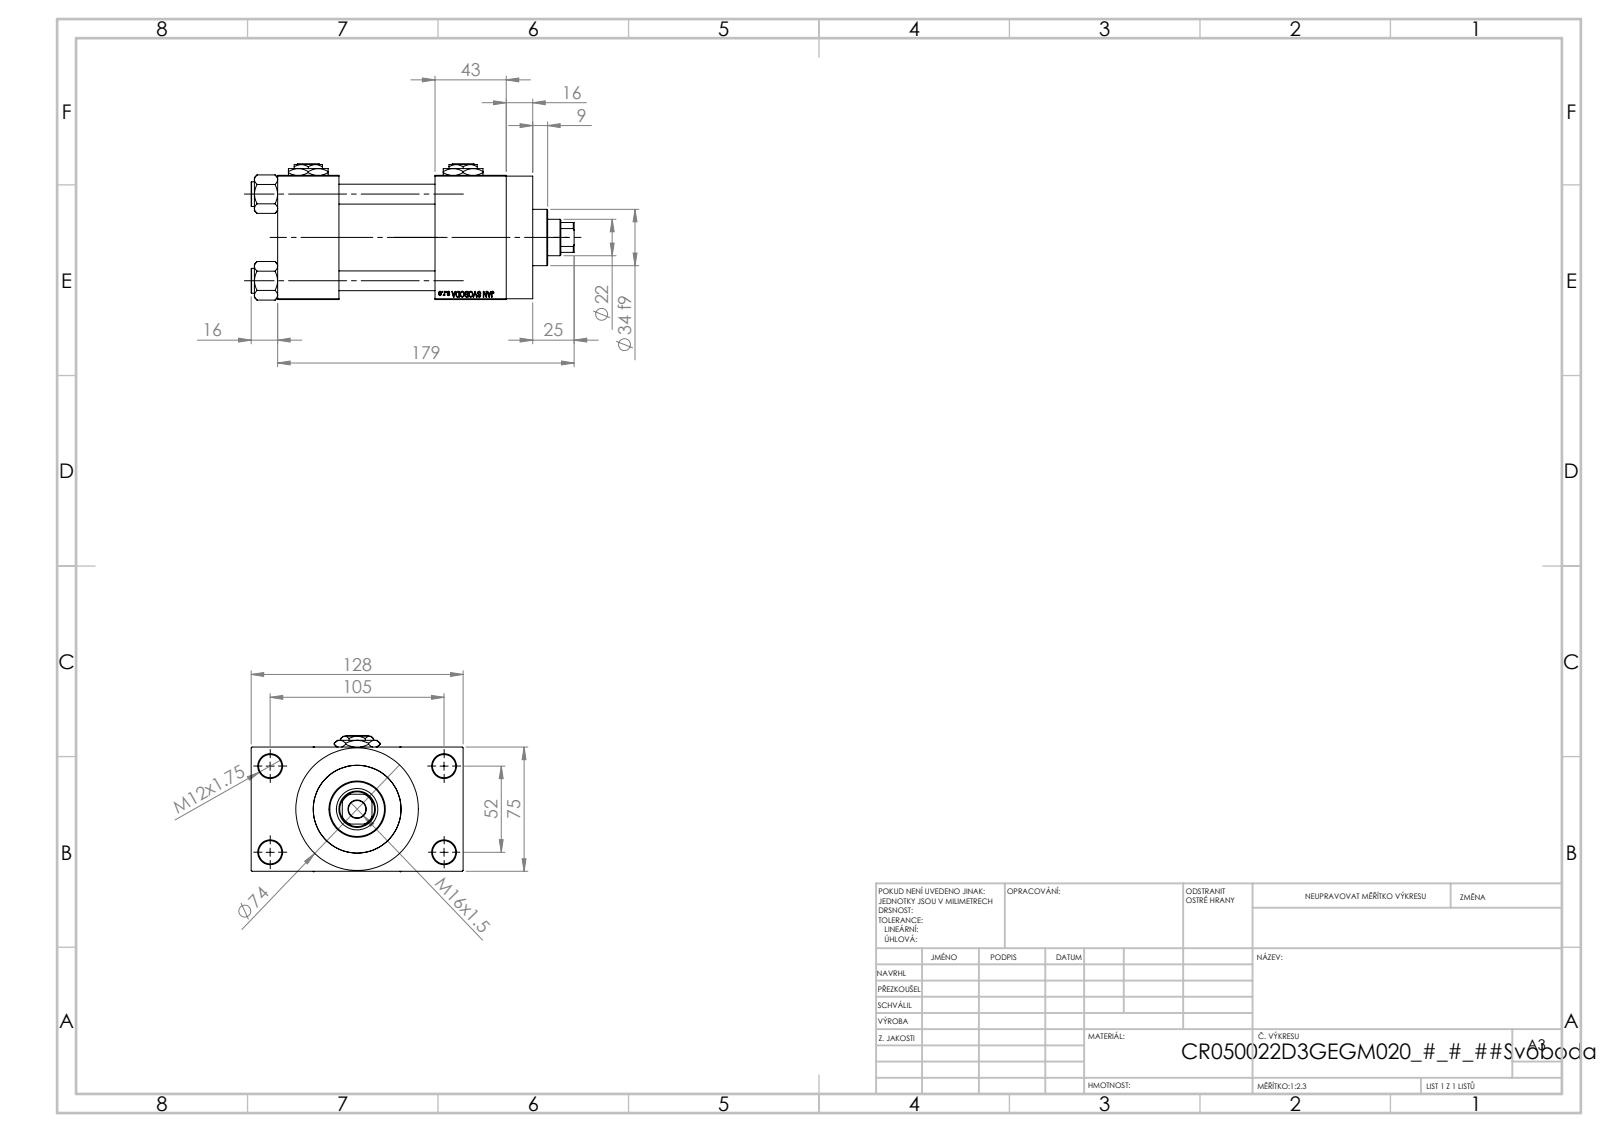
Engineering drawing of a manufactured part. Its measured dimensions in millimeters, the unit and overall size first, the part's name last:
Units: millimetres
Overall size (bounding box): 195 × 128 × 82.27
Round holes (diameter × count): ⌀12 ×4, ⌀14 ×4, ⌀7 ×2, ⌀20.96 ×2, ⌀30 ×2, ⌀10.5 ×1, ⌀22 ×1, ⌀25 ×1, ⌀41 ×1, ⌀50 ×1, ⌀53 ×1
Round bosses / shafts (diameter × count): ⌀15 ×4, ⌀74 ×1, ⌀56 ×1, ⌀34 ×1
Partial cylindrical surfaces — rounded edges, fillets, slot ends (radius × count): R10.5 ×1
Main face-to-face distances: 75, 58, 37, 95, 26.5, 101.5, 138, 101, 43, 16
Hole centre spacings: 26.35, 36.98, 52.3, 58.43, 58.59, 78.65, 94.37, 52
Volume: 802 177 mm³ · Surface area: 169 183 mm²
Bodies: 13 solids, 1205 faces (545 planar, 100 cylindrical, 560 other)
Part name (STEP PRODUCT): V215CR_VCP_D; V215CR_D_Body; NUT_M5_D; V215CR_D_TYCINKA (+2 more)
STEP written by: SolidWorks 2019 (CONFIG_CONTROL_DESIGN)
